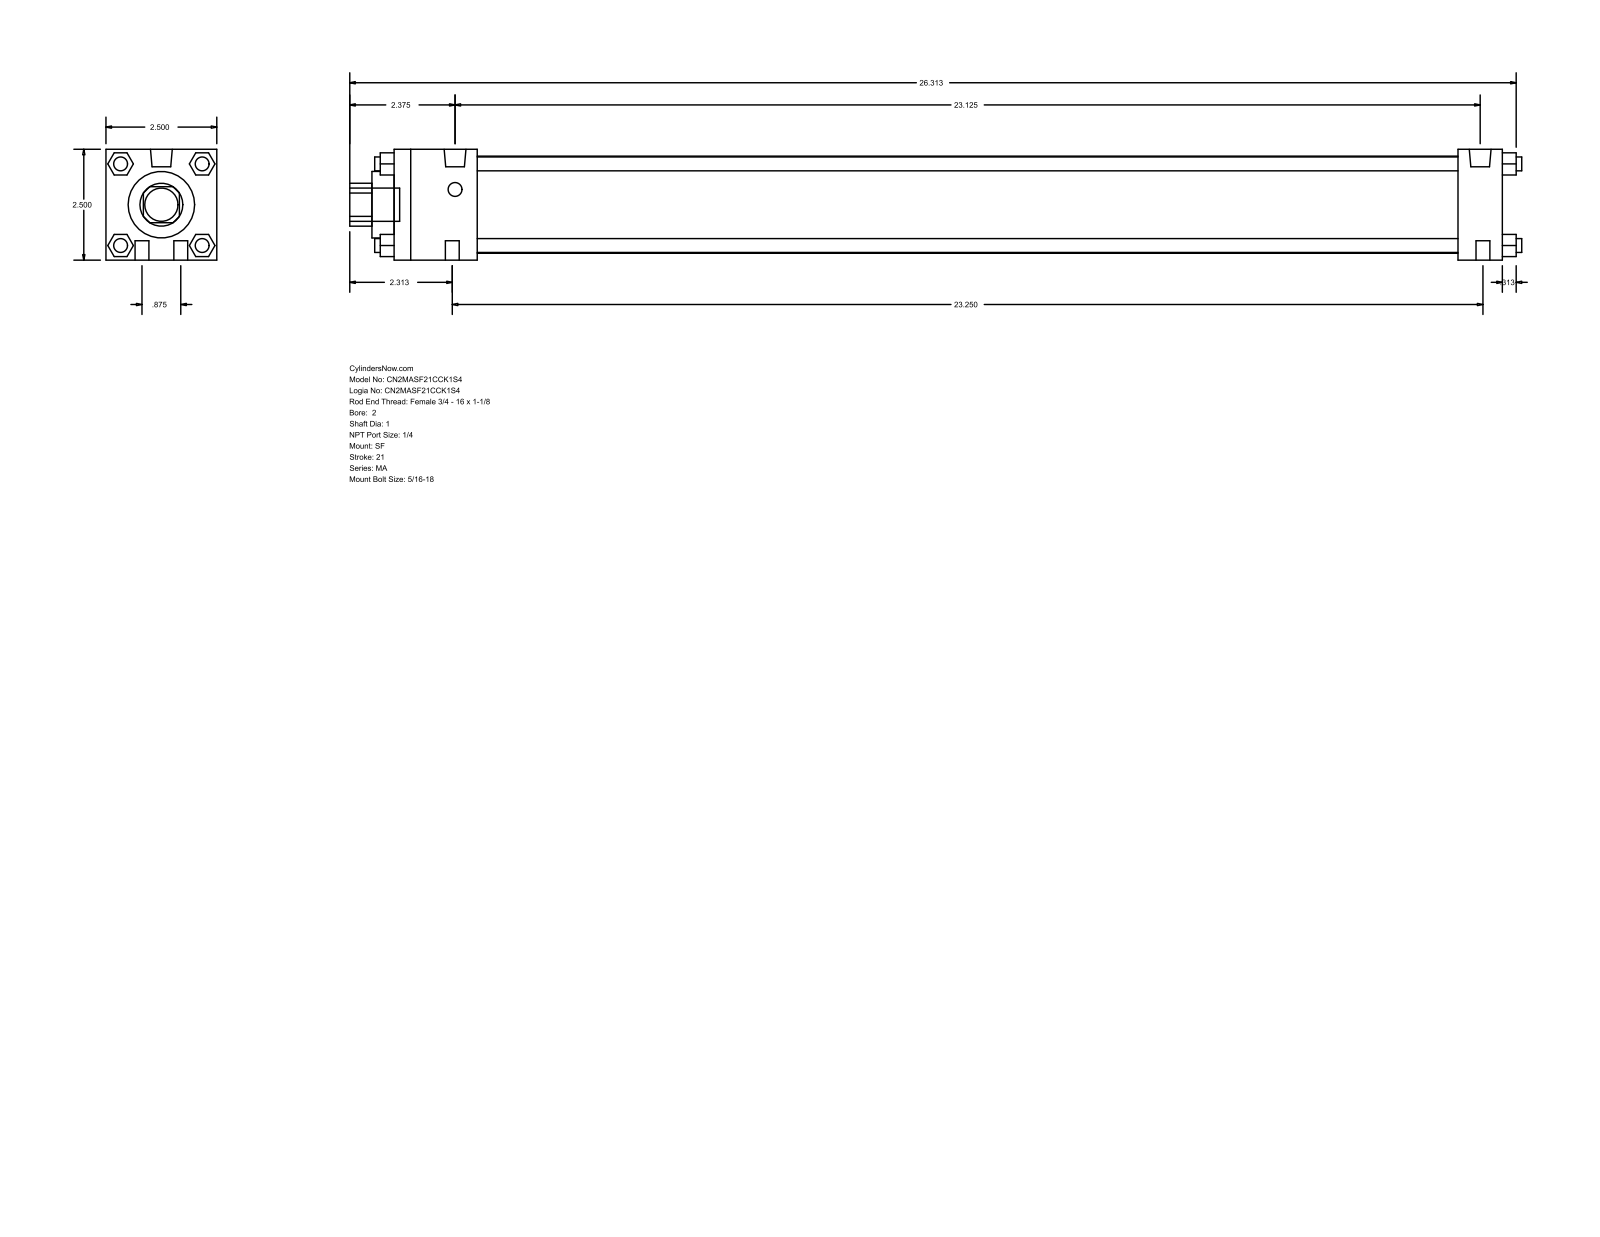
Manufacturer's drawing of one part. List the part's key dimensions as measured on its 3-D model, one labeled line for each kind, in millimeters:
Part name (STEP PRODUCT): MA_SF__0200_1
STEP written by: GSSL Pune (CONFIG_CONTROL_DESIGN)
Units: millimetres
Bodies: 0 solids, 124 faces (94 planar, 30 cylindrical, 0 other)
Overall size (bounding box): 671.51 × 63.5 × 63.5
Round holes (diameter × count): ⌀25.4 ×1, ⌀38.1 ×1, ⌀55.63 ×1
Round bosses / shafts (diameter × count): ⌀7.94 ×10, ⌀12.49 ×2, ⌀19.05 ×1
Partial cylindrical surfaces — rounded edges, fillets, slot ends (radius × count): R12.29 ×1
Main face-to-face distances: 63.5, 635, 12.7, 25.4, 609.6, 47.63, 561.97, 587.37, 40.47, 23.37
